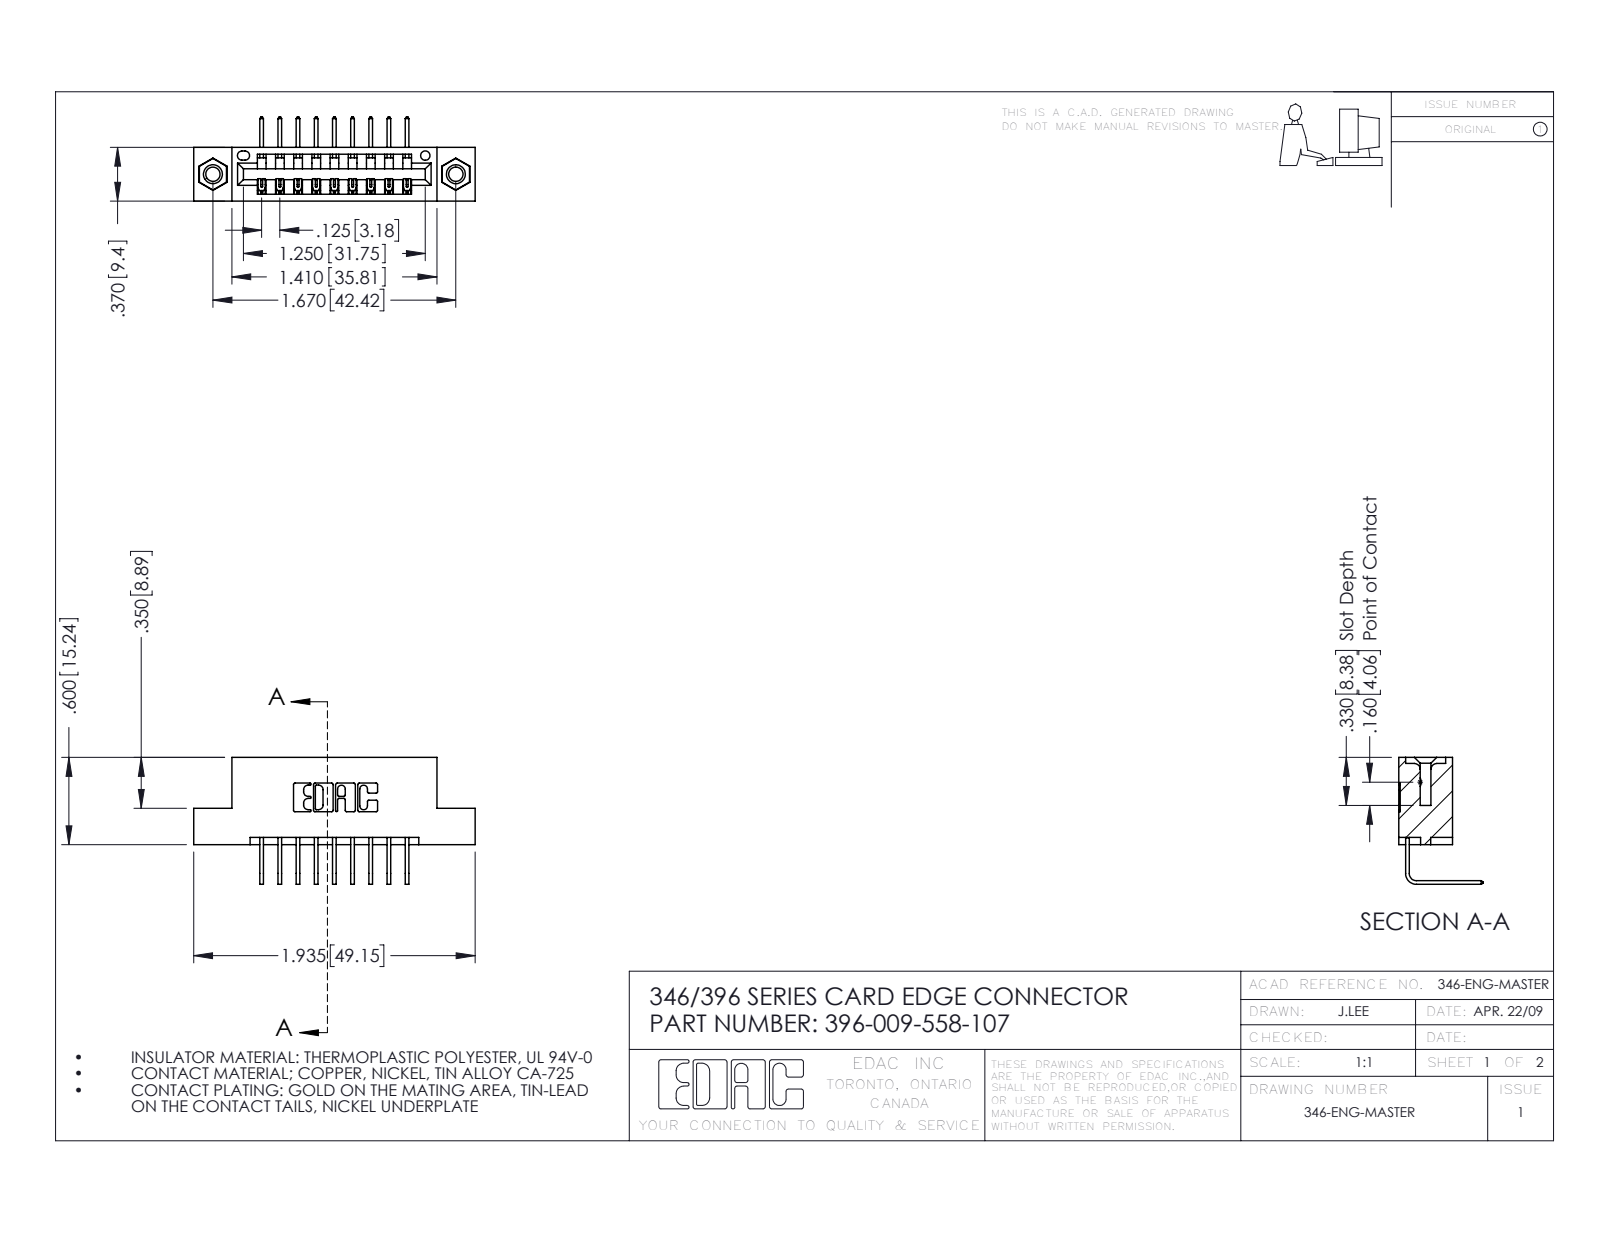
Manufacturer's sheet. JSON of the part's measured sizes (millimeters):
{"part_name": "396-009-558-107; 345-292-001_558 Tail - 2; 346 Part_Flush Mounting Lugs - 0.156 Dia-TI; 345-250-001_345-250-005-103", "step_written_by": "SolidWorks 2016 (CONFIG_CONTROL_DESIGN)", "units": "millimeters", "bodies": {"solids": 12, "faces": 722, "planar": 486, "cylindrical": 220, "other": 16}, "overall_size": [49.1, 22.2, 14.7], "volume_mm3": 4490, "surface_area_mm2": 5474, "round_holes": [[2.5, 2], [3.2, 2], [4, 2], [1.6, 1]], "round_bosses_or_shafts": [[3.9, 2]], "partial_cylinders_radius": [[0.3, 22], [0.2, 18], [0.2, 6], [0.8, 6], [0.7, 3], [0.8, 2], [1, 2], [0.4, 1]], "face_to_face_distances": [6.4, 8.2, 9.4, 1.2, 7.6, 0.6, 3.8, 5.6, 2.5, 4.4], "hole_center_spacings": [6.2, 37.2, 42.4]}
